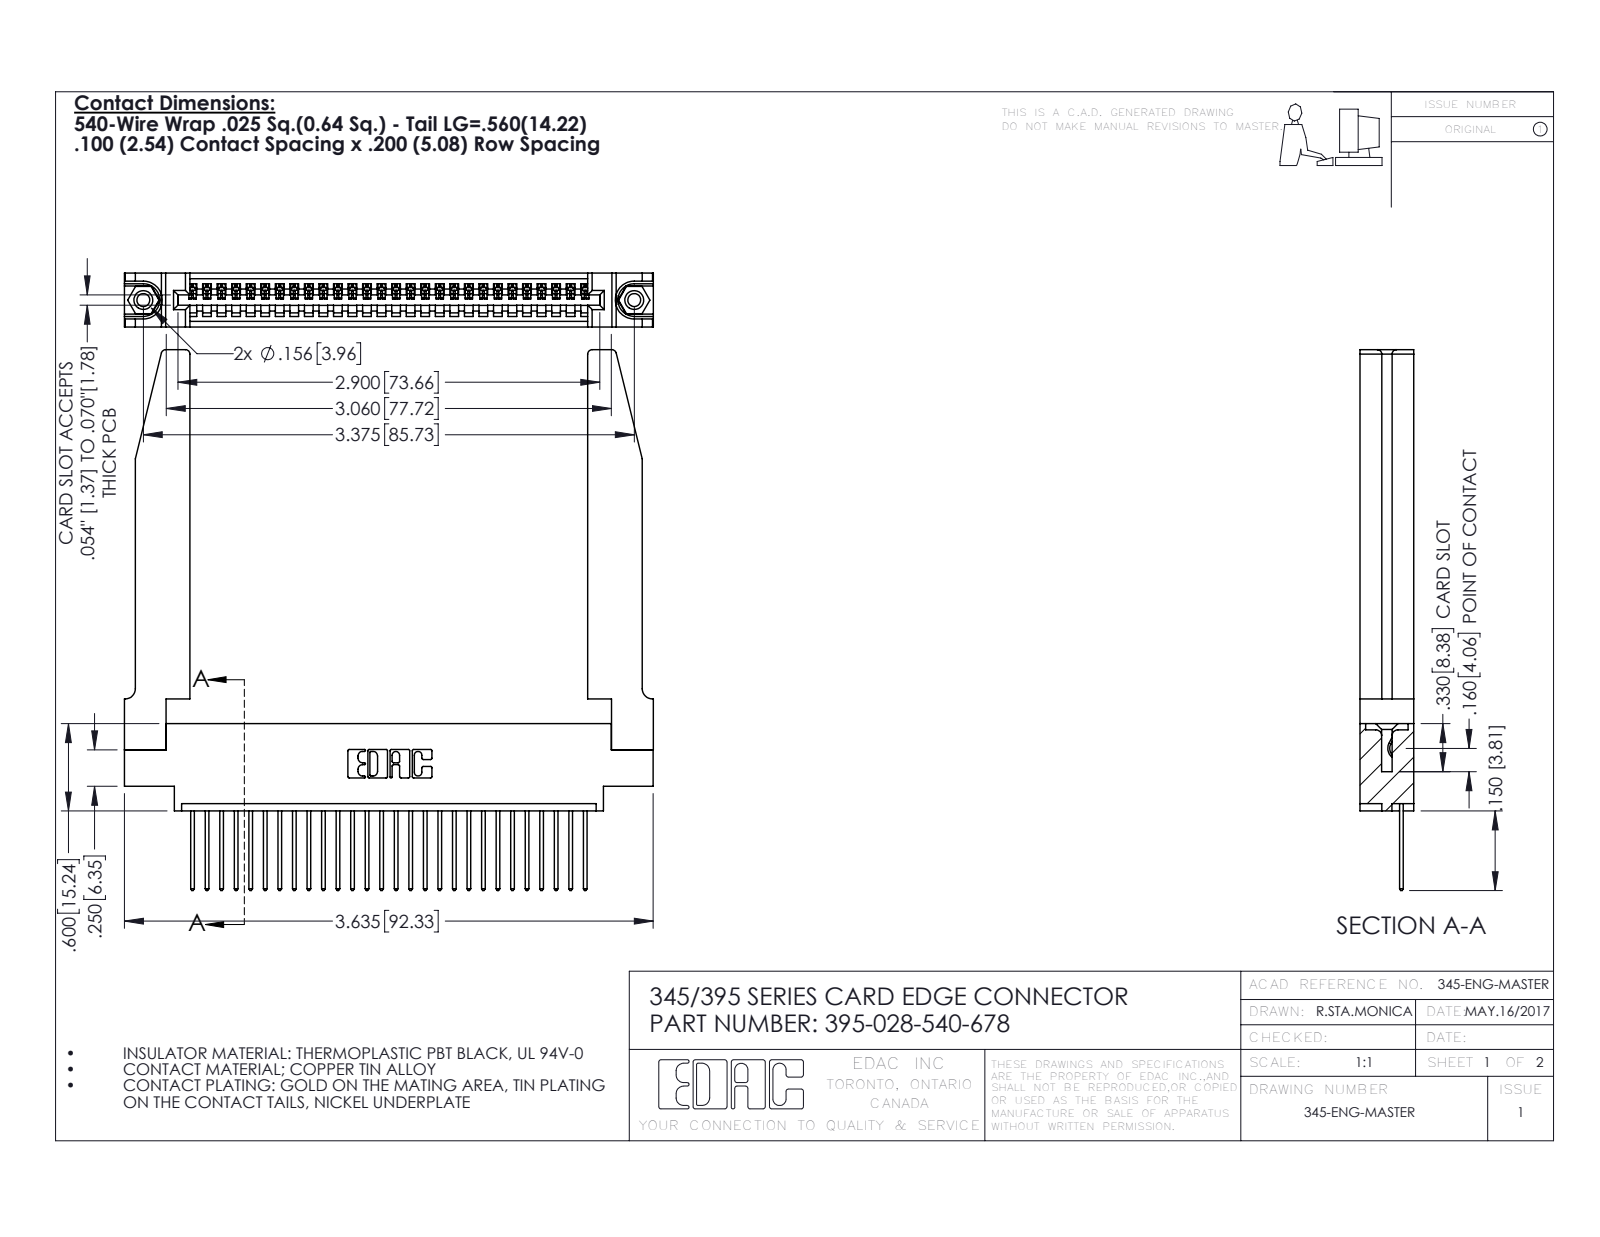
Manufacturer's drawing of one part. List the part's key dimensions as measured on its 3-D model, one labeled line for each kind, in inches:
Part name (STEP PRODUCT): 345 Part_0.170 Offset - 0.156 Dia-TH; 345-292-001_345-293-140; 395-028-540-678; 345-220-078_345-220-078 (+1 more)
STEP written by: SolidWorks 2016 (CONFIG_CONTROL_DESIGN)
Units: inches
Bodies: 33 solids, 1988 faces (1346 planar, 590 cylindrical, 52 other)
Overall size (bounding box): 3.717 × 3.636 × 0.37
Volume: 0.998 in³ · Surface area: 28.61 in²
Round holes (diameter × count): ⌀0.089 ×2, ⌀0.125 ×2, ⌀0.156 ×2, ⌀0.064 ×1
Round bosses / shafts (diameter × count): ⌀0.155 ×2
Partial cylindrical surfaces — rounded edges, fillets, slot ends (radius × count): R0.006 ×56, R0.01 ×56, R0.01 ×22, R0.03 ×8, R0.007 ×6, R0.031 ×6, R0.026 ×3, R0.031 ×2
Main face-to-face distances: 0.37, 0.072, 0.298, 0.098, 0.272, 0.025, 0.2, 0.148, 0.15, 0.225
Hole centre spacings: 0.27, 3.14, 3.375
